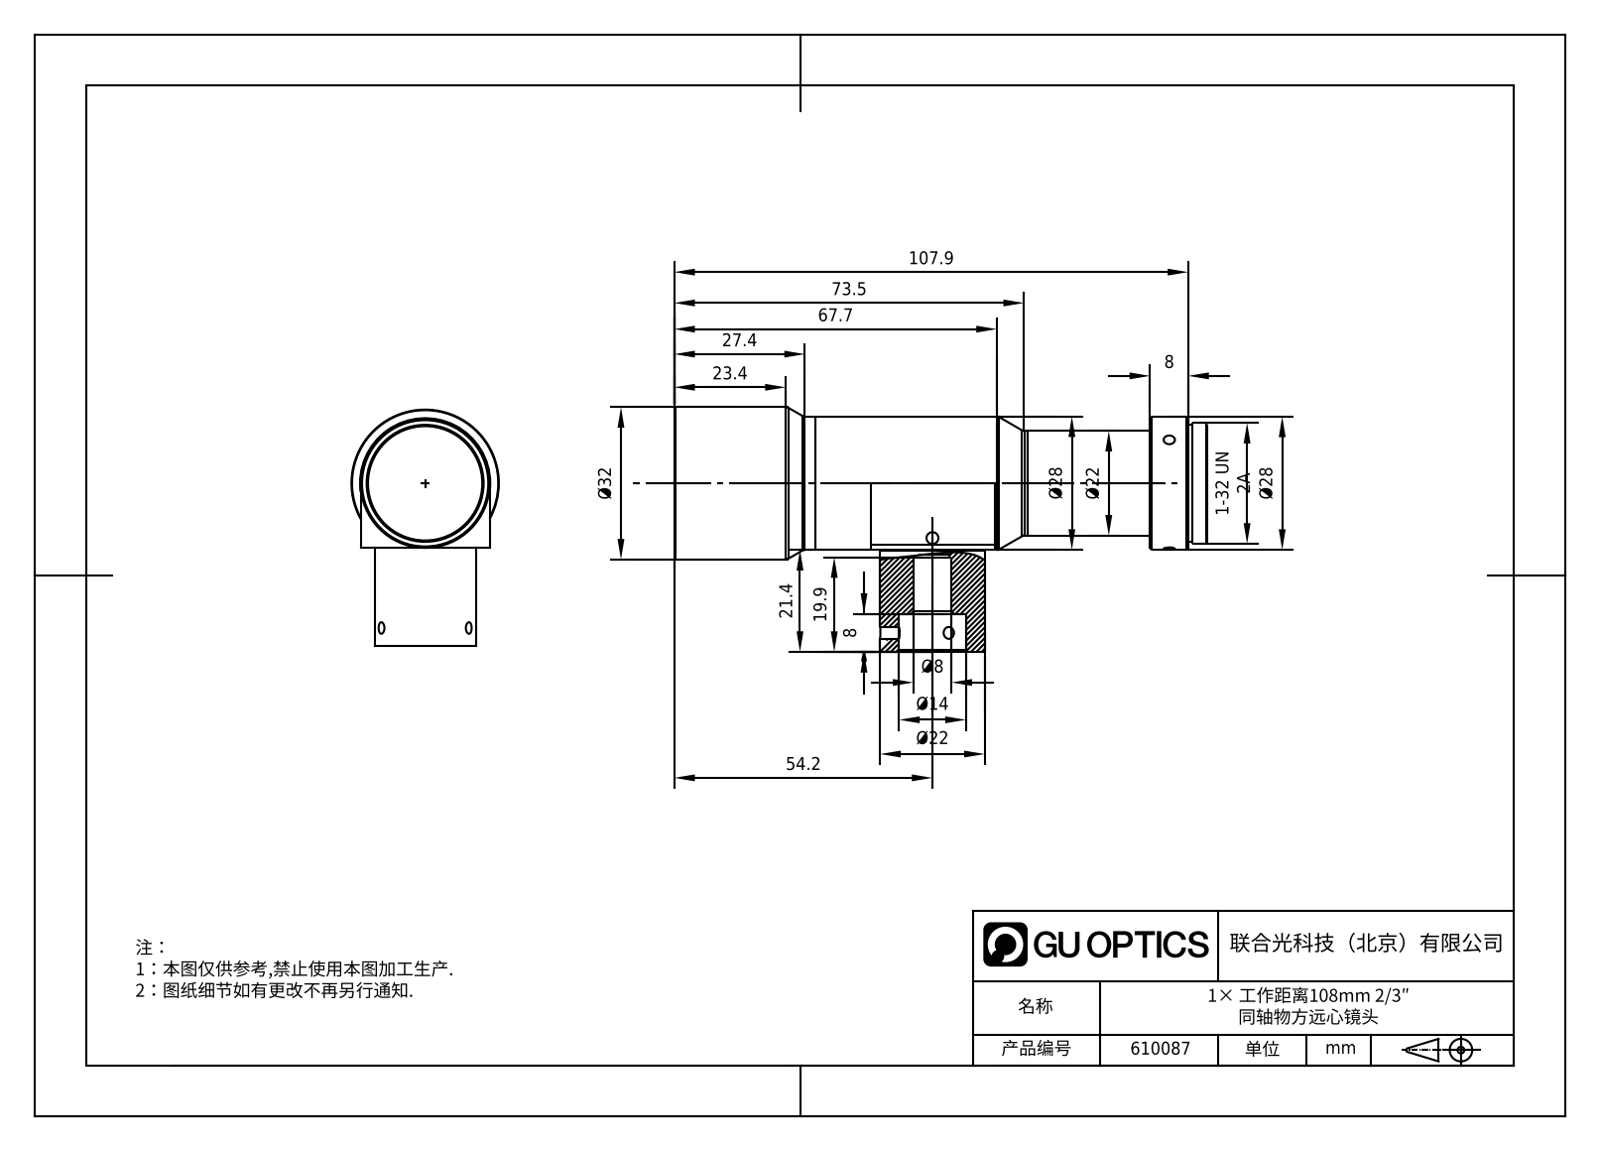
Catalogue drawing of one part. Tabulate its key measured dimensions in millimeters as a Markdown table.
| quantity | value |
| --- | --- |
| part name | WWH10-108CTV3 |
| STEP written by | SolidWorks 2017 (CONFIG_CONTROL_DESIGN) |
| units | millimeters |
| bodies | 1 solid, 60 faces (15 planar, 25 cylindrical, 20 other) |
| overall size | 111.9 × 51.4 × 32 |
| volume | 74 629 mm³ |
| surface area | 14 068 mm² |
| round holes (diameter × count) | 2.5 × 3, 8 × 1, 14 × 1 |
| round bosses / shafts (diameter × count) | 22 × 2, 32 × 1, 28 × 1, 25.4 × 1, 24.4 × 1 |
| main face-to-face distances | 111.9, 28, 21.4, 8, 99.9, 12, 107.9, 4, 13.4, 41.2 |
